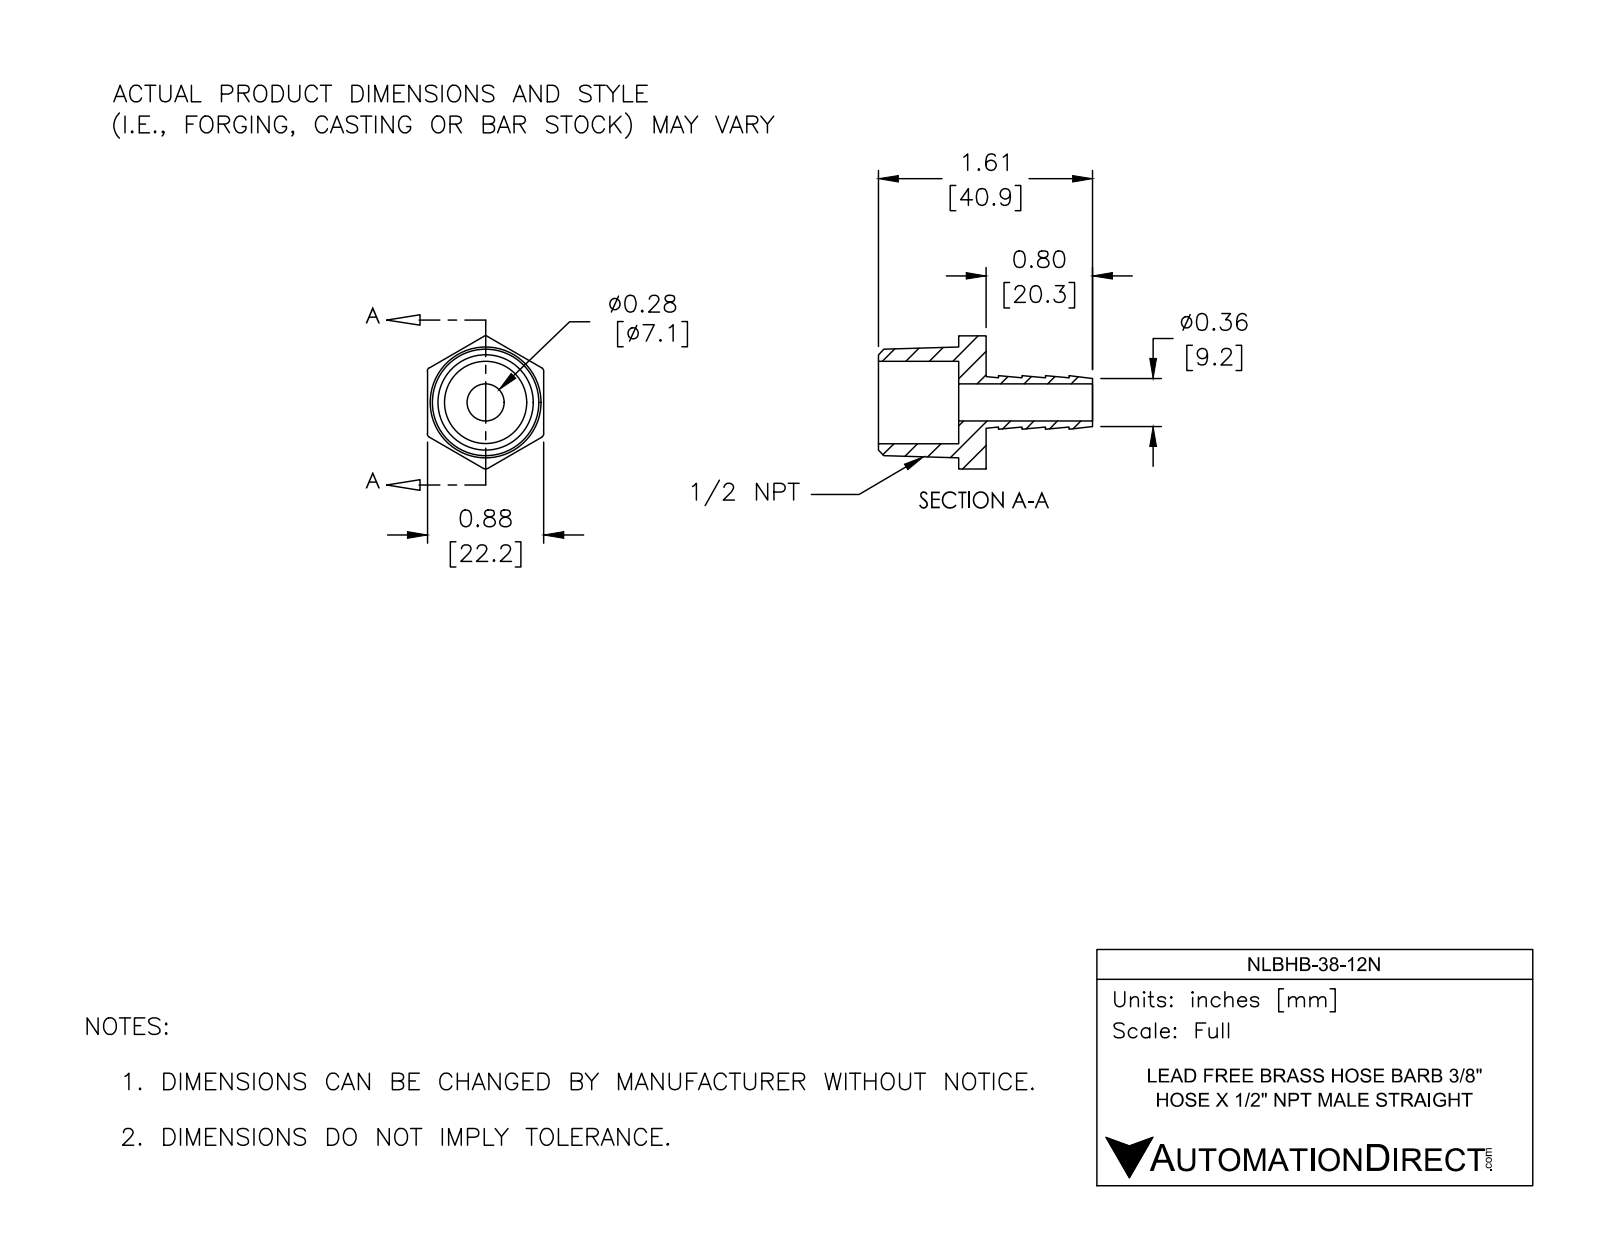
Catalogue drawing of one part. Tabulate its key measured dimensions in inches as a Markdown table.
| quantity | value |
| --- | --- |
| part name | NLBHB-38-12N |
| STEP written by | SolidWorks 2017 (AUTOMOTIVE_DESIGN) |
| units | inches |
| bodies | 1 solid, 39 faces (15 planar, 10 cylindrical, 14 other) |
| overall size | 1.61 × 1.001 × 0.875 |
| volume | 0.3 in³ |
| surface area | 6.375 in² |
| round holes (diameter × count) | 0.28 × 1, 0.62 × 1 |
| partial cylindrical surfaces (radius × count) | 0.03 × 6 |
| main face-to-face distances | 0.206, 0.875, 0.81, 0.604, 0.177, 0.8, 1.006, 1.61, 0.531, 0.354 |
